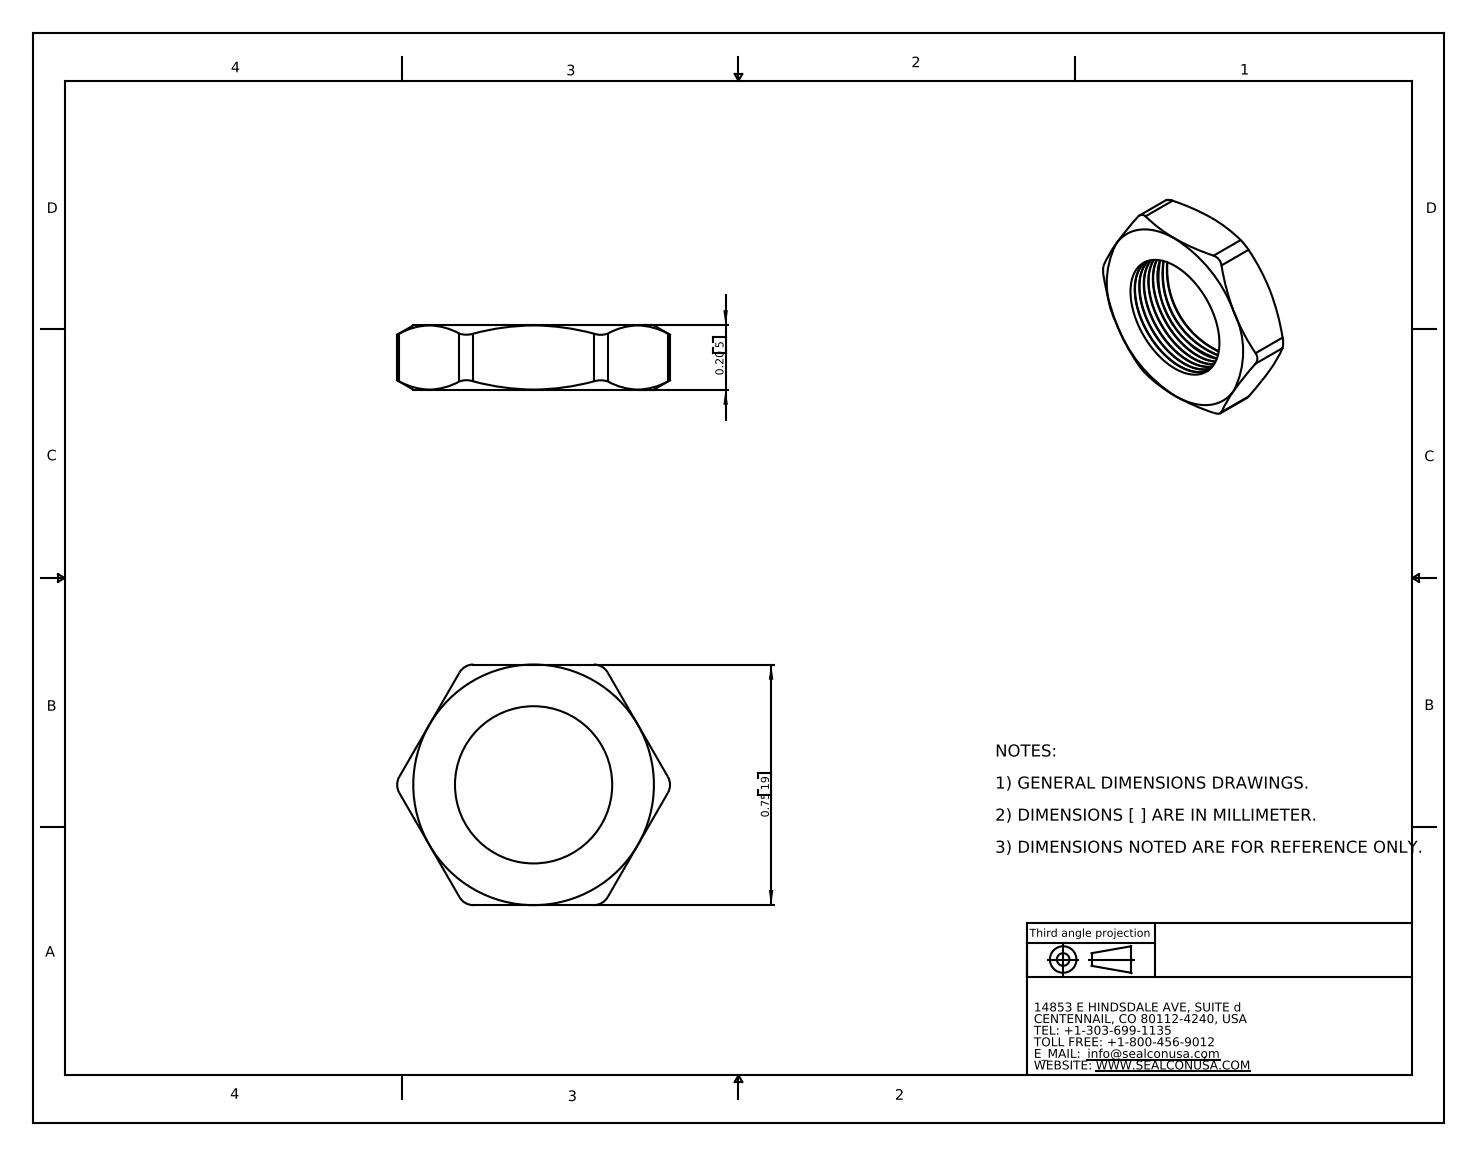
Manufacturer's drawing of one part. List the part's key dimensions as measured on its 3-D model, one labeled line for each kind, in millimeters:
Part name (STEP PRODUCT): NP-07
STEP written by: SolidWorks 2007 (CONFIG_CONTROL_DESIGN)
Units: millimetres
Bodies: 1 solid, 77 faces (8 planar, 23 cylindrical, 46 other)
Overall size (bounding box): 21.6 × 19.1 × 5.1
Volume: 920 mm³ · Surface area: 1 085 mm²
Round holes (diameter × count): ⌀12.4 ×1
Partial cylindrical surfaces — rounded edges, fillets, slot ends (radius × count): R1.3 ×6
Main face-to-face distances: 5.1, 19.1
